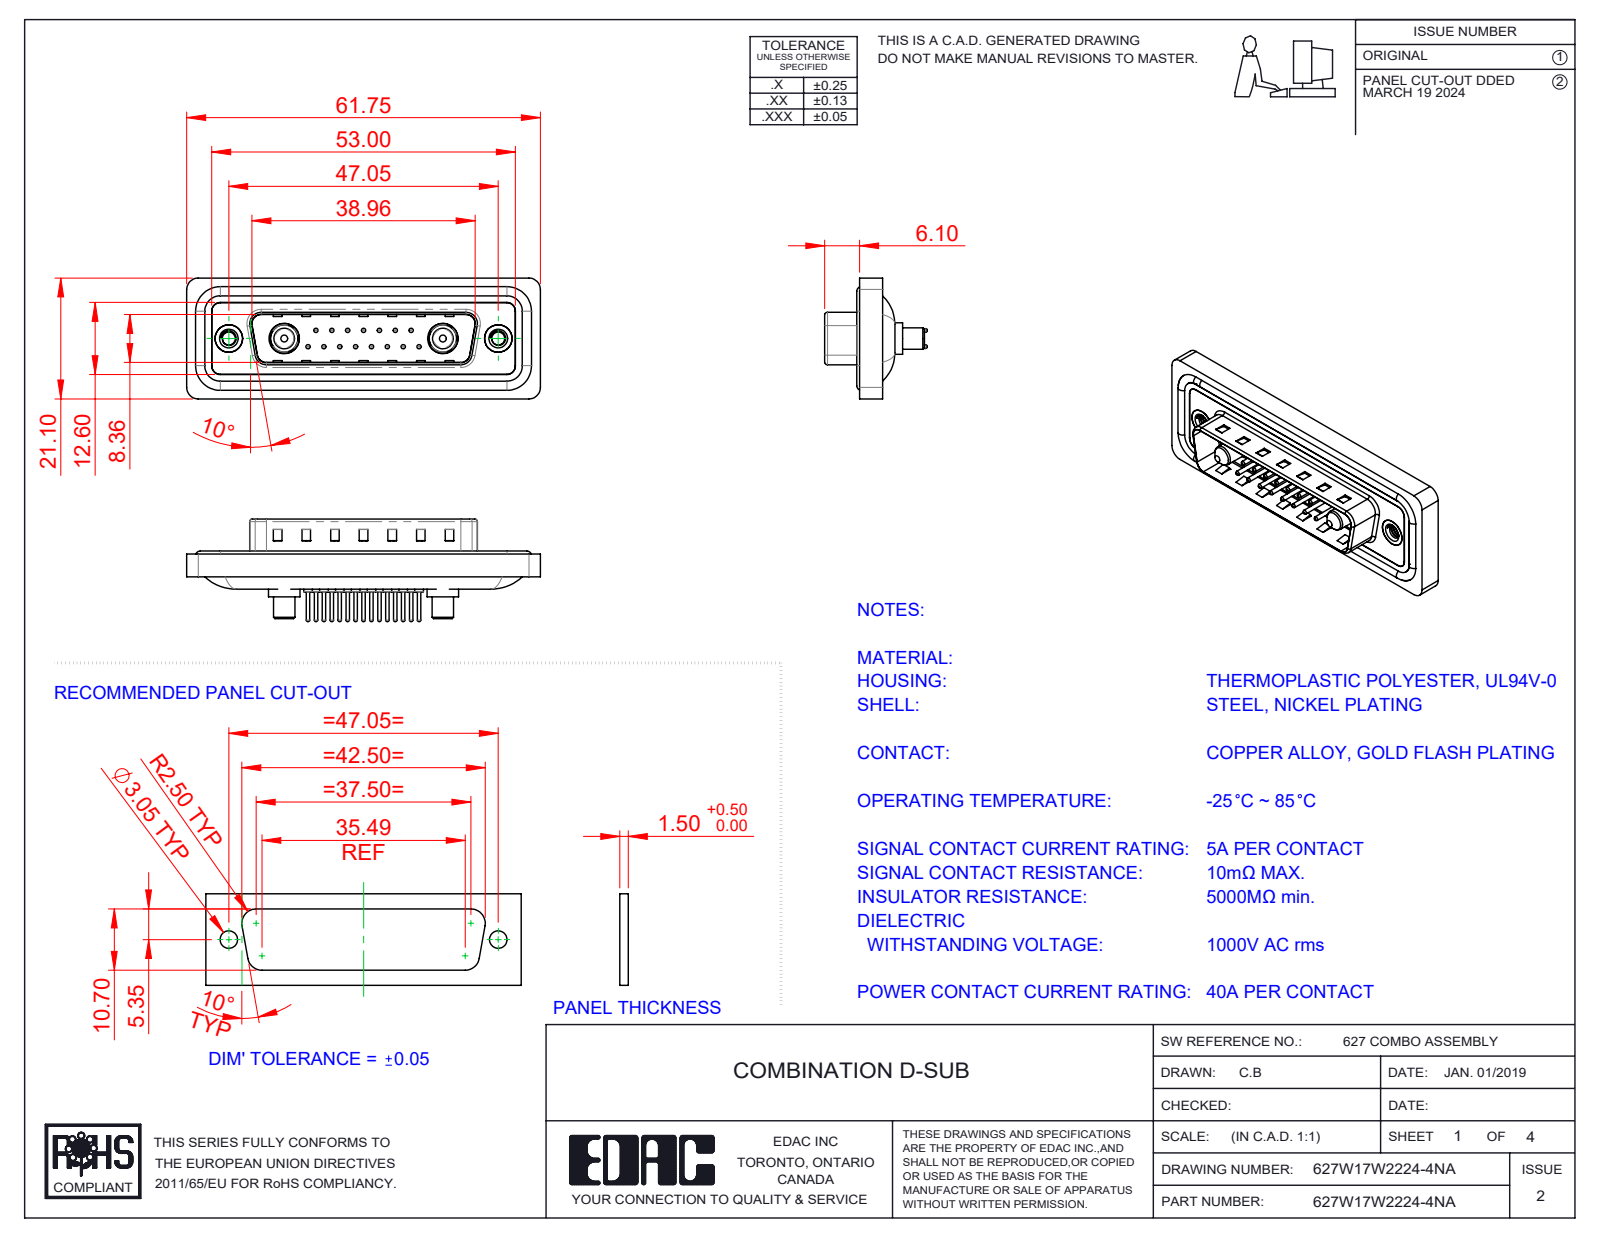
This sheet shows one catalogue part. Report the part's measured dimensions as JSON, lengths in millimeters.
{"part_name": "627Combo Waterproof Housing_25 Contacts; 627W17W2224-4NA; 627Combo Shell Front_25 Contacts; 627Combo Threaded Rivet_A (+5 more)", "step_written_by": "SolidWorks 2023 (CONFIG_CONTROL_DESIGN)", "units": "millimeters", "bodies": {"solids": 26, "faces": 1114, "planar": 334, "cylindrical": 438, "other": 342}, "overall_size": [61.75, 21.1, 17.9], "volume_mm3": 7305, "surface_area_mm2": 11933, "round_holes": [[0.75, 15], [1.6, 15], [2, 15], [2.26, 2], [4, 2], [4.8, 2], [4.85, 2], [5, 2], [5.3, 2]], "round_bosses_or_shafts": [[1.5, 15], [0.6, 15], [1.6, 4], [5.5, 2], [5.2, 2], [4.9, 2], [4.75, 2], [3.75, 2]], "partial_cylinders_radius": [[1.5, 22], [2, 18], [0.5, 8], [1.6, 8], [0.25, 4], [0.6, 4], [0.65, 4], [0.9, 4]], "face_to_face_distances": [0.4, 1.5, 1.1, 1.6, 0.5, 3.1, 2.9, 0.82, 9.58, 4.1], "hole_center_spacings": [3.16, 2.77, 5.54, 8.31, 5.04, 7.49, 11.08, 5.03]}
